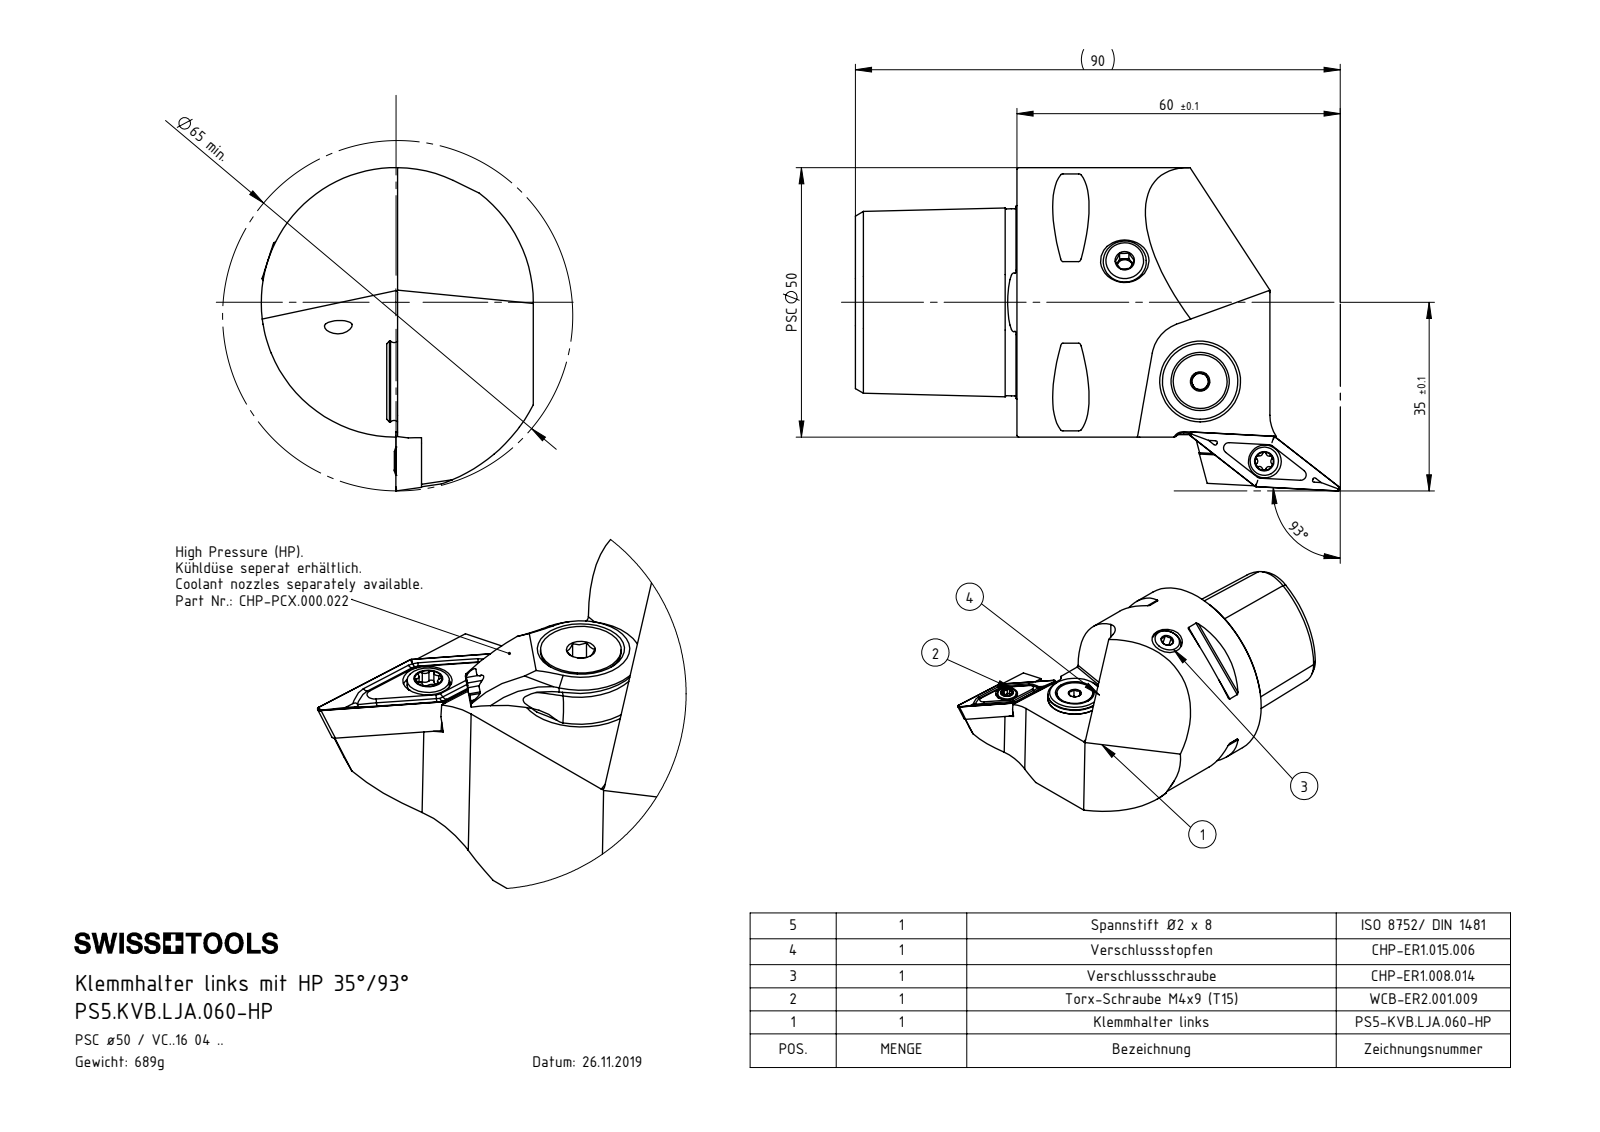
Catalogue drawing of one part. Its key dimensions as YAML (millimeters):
part_name: "ISO 8752 2x8; PS5-KVB.LJA.060-HP_A; WCB-ER2.001.009_A; DIN 3771 - 13x1 (+6 more)"
step_written_by: "SolidWorks 2017 (AUTOMOTIVE_DESIGN)"
units: millimeters
bodies: {solids: 8, faces: 278, planar: 94, cylindrical: 62, other: 122}
overall_size: [90, 60, 50.5]
volume: 87663
surface_area: 21391
round_holes:
  - {diameter: 4.2, count: 2}
  - {diameter: 5, count: 2}
  - {diameter: 6.1, count: 2}
  - {diameter: 1.2, count: 1}
  - {diameter: 2, count: 1}
  - {diameter: 2.5, count: 1}
  - {diameter: 3, count: 1}
  - {diameter: 3.3, count: 1}
  - {diameter: 4, count: 1}
  - {diameter: 4.4, count: 1}
  - {diameter: 5.2, count: 1}
  - {diameter: 7, count: 1}
round_bosses_or_shafts:
  - {diameter: 50, count: 1}
  - {diameter: 15, count: 1}
  - {diameter: 13.4, count: 1}
  - {diameter: 10, count: 1}
  - {diameter: 8, count: 1}
  - {diameter: 5.5, count: 1}
  - {diameter: 5.25, count: 1}
  - {diameter: 5, count: 1}
partial_cylinders:
  - {radius: 0.5, count: 8}
  - {radius: 0.34, count: 6}
  - {radius: 0.59, count: 6}
  - {radius: 0.4, count: 2}
  - {radius: 7, count: 2}
  - {radius: 1.75, count: 1}
  - {radius: 4, count: 1}
  - {radius: 25.5, count: 1}
face_to_face_distances: [30, 4.5, 4.46, 20.7, 20.74, 25.2, 19.18, 44.4, 10, 20]
hole_center_spacings: [4.5, 16.55, 16.63, 18.99, 19.09, 26, 26.45, 30.29]
